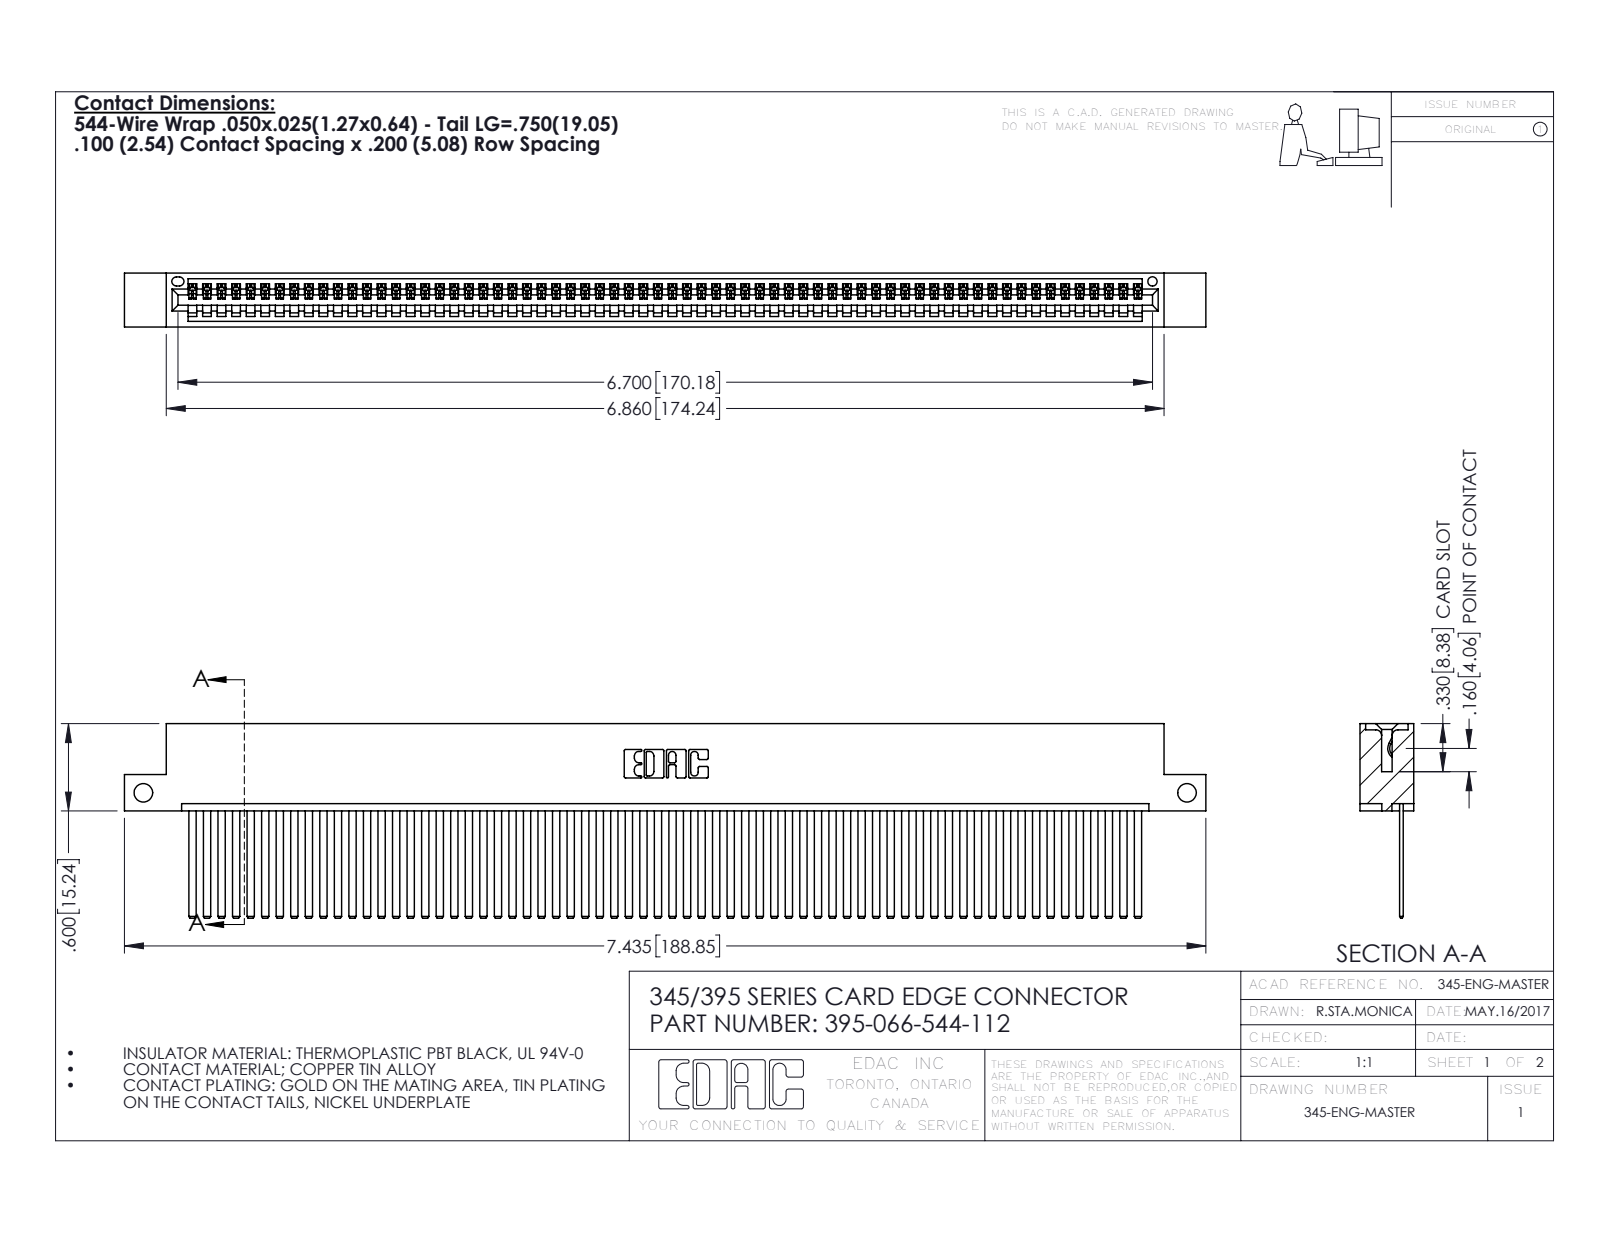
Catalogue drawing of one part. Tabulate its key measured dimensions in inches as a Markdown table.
| quantity | value |
| --- | --- |
| part name | 345-292-001_345-293-144; 395-066-544-112; 345 Part_Flush Mounting Lugs - Side Mount |
| STEP written by | SolidWorks 2016 (CONFIG_CONTROL_DESIGN) |
| units | inches |
| bodies | 67 solids, 3558 faces (2456 planar, 1102 cylindrical, 0 other) |
| overall size | 7.435 × 1.337 × 0.37 |
| volume | 1.148 in³ |
| surface area | 42.59 in² |
| round holes (diameter × count) | 0.128 × 2, 0.064 × 1 |
| partial cylindrical surfaces (radius × count) | 0.006 × 132, 0.01 × 22, 0.007 × 6, 0.031 × 6, 0.026 × 3, 0.031 × 2, 0.04 × 2, 0.014 × 1 |
| main face-to-face distances | 0.072, 0.298, 0.025, 0.098, 0.272, 0.37, 0.2, 0.225, 0.149, 0.072 |
| hole center spacings | 7.175 |
